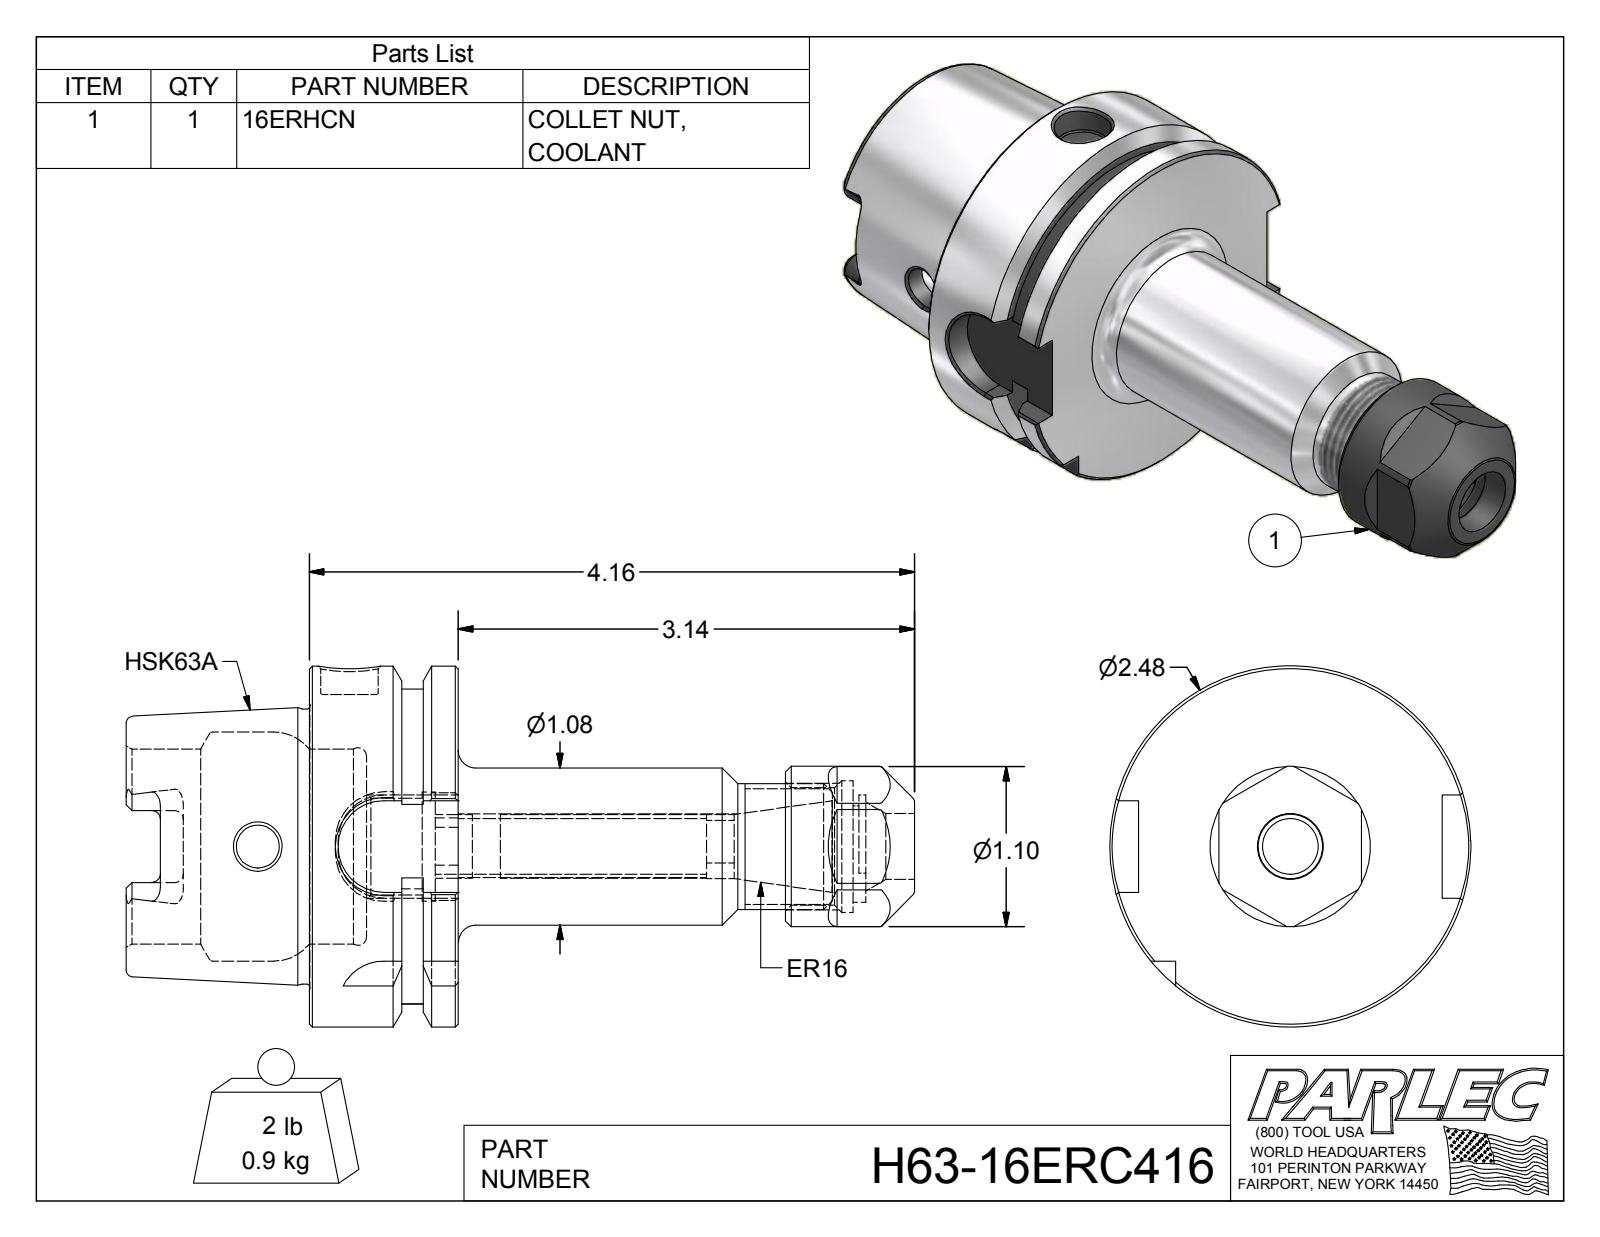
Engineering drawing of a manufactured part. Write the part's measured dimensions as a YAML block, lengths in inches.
part_name: "H63-16ERC416; H63-16ER4-1; 16ERHCN"
step_written_by: "Autodesk Inventor 2012 (AUTOMOTIVE_DESIGN)"
units: inches
bodies: {solids: 2, faces: 173, planar: 74, cylindrical: 42, other: 57}
overall_size: [5.42, 2.48, 2.48]
volume: 7.066
surface_area: 52.02
round_holes:
  - {diameter: 0.295, count: 1}
  - {diameter: 0.383, count: 1}
  - {diameter: 0.394, count: 1}
  - {diameter: 0.44, count: 1}
  - {diameter: 0.453, count: 1}
  - {diameter: 0.661, count: 1}
  - {diameter: 0.666, count: 1}
  - {diameter: 0.749, count: 1}
  - {diameter: 0.807, count: 1}
  - {diameter: 0.906, count: 1}
  - {diameter: 1.339, count: 1}
  - {diameter: 1.575, count: 1}
round_bosses_or_shafts:
  - {diameter: 2.48, count: 1}
  - {diameter: 1.891, count: 1}
  - {diameter: 1.102, count: 1}
  - {diameter: 1.08, count: 1}
  - {diameter: 0.866, count: 1}
partial_cylinders:
  - {radius: 0.059, count: 6}
  - {radius: 0.113, count: 4}
  - {radius: 0.315, count: 4}
  - {radius: 0.191, count: 1}
  - {radius: 0.354, count: 1}
  - {radius: 1.083, count: 1}
face_to_face_distances: [1.024, 0.241, 0.389, 0.394, 0.63, 1.26, 1.654, 2.283, 0.979, 2.043]
hole_center_spacings: [0.051]
